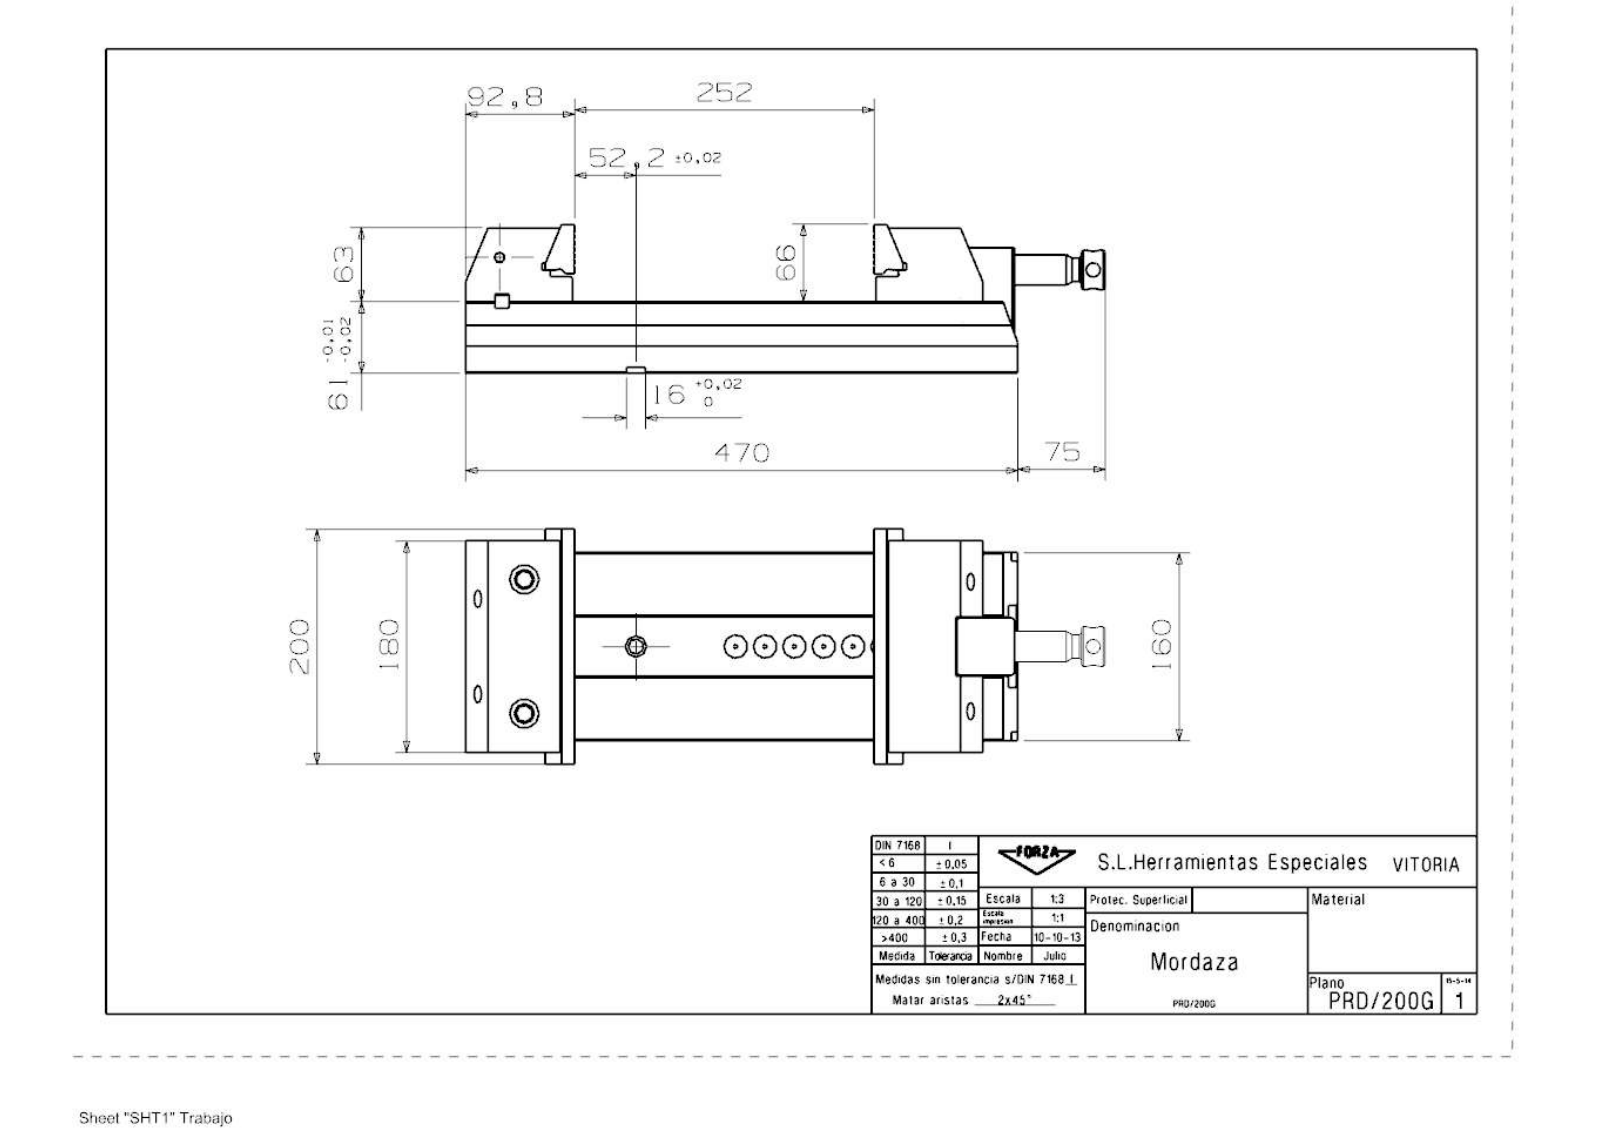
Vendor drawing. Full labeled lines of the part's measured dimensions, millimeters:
Part name (STEP PRODUCT): PRD_200G_Mordaza
STEP written by: SIEMENS PLM Software NX 9.0 (CONFIG_CONTROL_DESIGN)
Units: millimetres
Bodies: 11 solids, 481 faces (295 planar, 126 cylindrical, 60 other)
Overall size (bounding box): 544.42 × 200 × 126.95
Volume: 5 516 000 mm³ · Surface area: 589 946 mm²
Round holes (diameter × count): ⌀15 ×6, ⌀5.19 ×5, ⌀13 ×5, ⌀6.99 ×4, ⌀8.5 ×4, ⌀10 ×4, ⌀14.38 ×4, ⌀8.78 ×3, ⌀19 ×3, ⌀12 ×2, ⌀12.38 ×2, ⌀17 ×2
Round bosses / shafts (diameter × count): ⌀34 ×1, ⌀33.8 ×1, ⌀26 ×1, ⌀20 ×1, ⌀16.5 ×1
Partial cylindrical surfaces — rounded edges, fillets, slot ends (radius × count): R0.4 ×24, R8 ×4, R20 ×4, R1.6 ×2, R6 ×2, R7 ×2, R4 ×1, R9 ×1
Main face-to-face distances: 61, 29.2, 31.8, 63, 124, 94.8, 10, 160, 1.1, 28.1
Hole centre spacings: 14.5, 95.5, 81, 110, 68, 16.47, 16.55, 24.52
